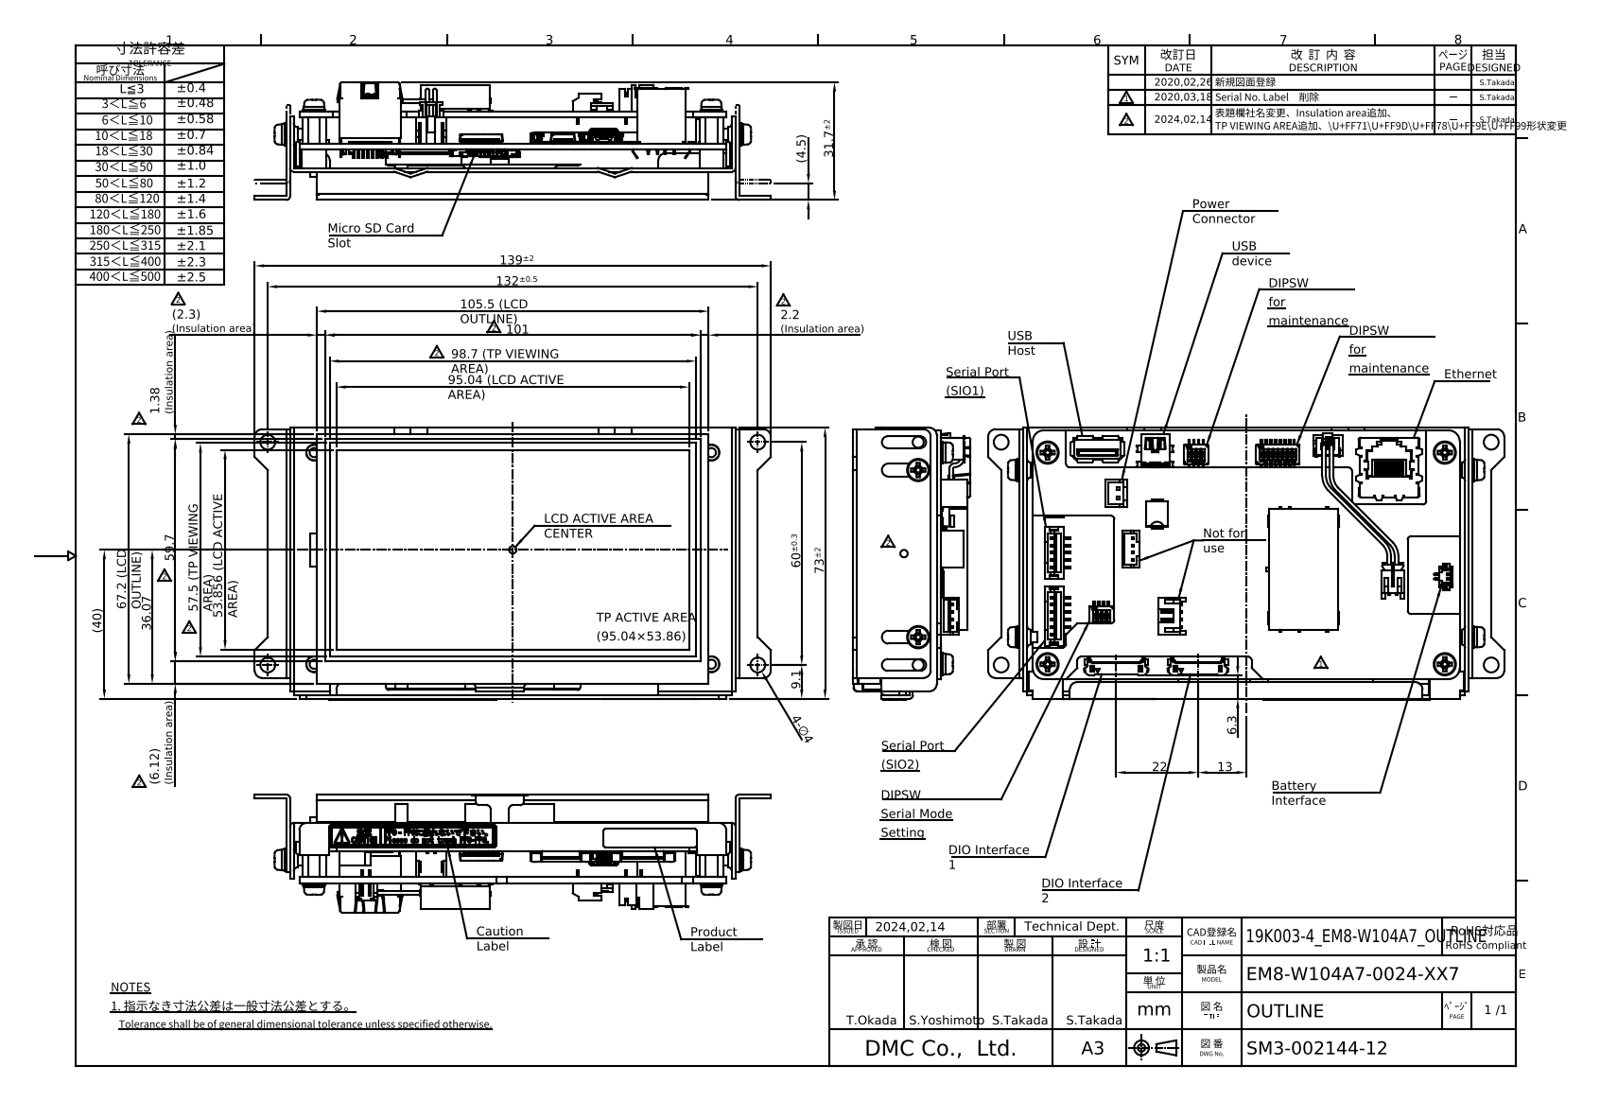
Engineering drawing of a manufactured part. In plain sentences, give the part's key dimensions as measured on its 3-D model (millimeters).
The part is named "HP_EM8-W104A7-0024-207". Its 3-D file was written by "Autodesk Inventor 2020 (AUTOMOTIVE_DESIGN)". It is 1 solid with 7990 faces: 6019 planar, 1312 cylindrical and 659 other. Overall it measures 139 by 73.2 by 31.72 millimeters. Its volume is 101 634 cubic millimeters and its surface area 91 012 square millimeters. Round holes: 6 of diameter 4, 4 of diameter 2.46, 4 of diameter 3.5, 4 of diameter 4.25, 3 of diameter 1.2, 1 of diameter 0.3, 1 of diameter 1.33, 1 of diameter 2. Round bosses or shafts: 10 of diameter 1, 8 of diameter 3, 6 of diameter 6, 6 of diameter 5.5, 4 of diameter 6.5, 4 of diameter 4.24, 3 of diameter 3.7, 2 of diameter 8. Partial cylindrical surfaces (rounded edges, fillets, slot ends): 259 of radius 0.1, 92 of radius 0.2, 67 of radius 0.3, 62 of radius 0.15, 40 of radius 0.5, 35 of radius 1, 21 of radius 0.25, 20 of radius 2. The main face-to-face distances are 8.6, 1.6, 6.6, 1, 15.22, 8.62, 5, 13.62, 13.82, 1.4. The hole center spacings are 12.5, 12.81, 57, 58.55, 60, 61.09, 107, 119.5.
